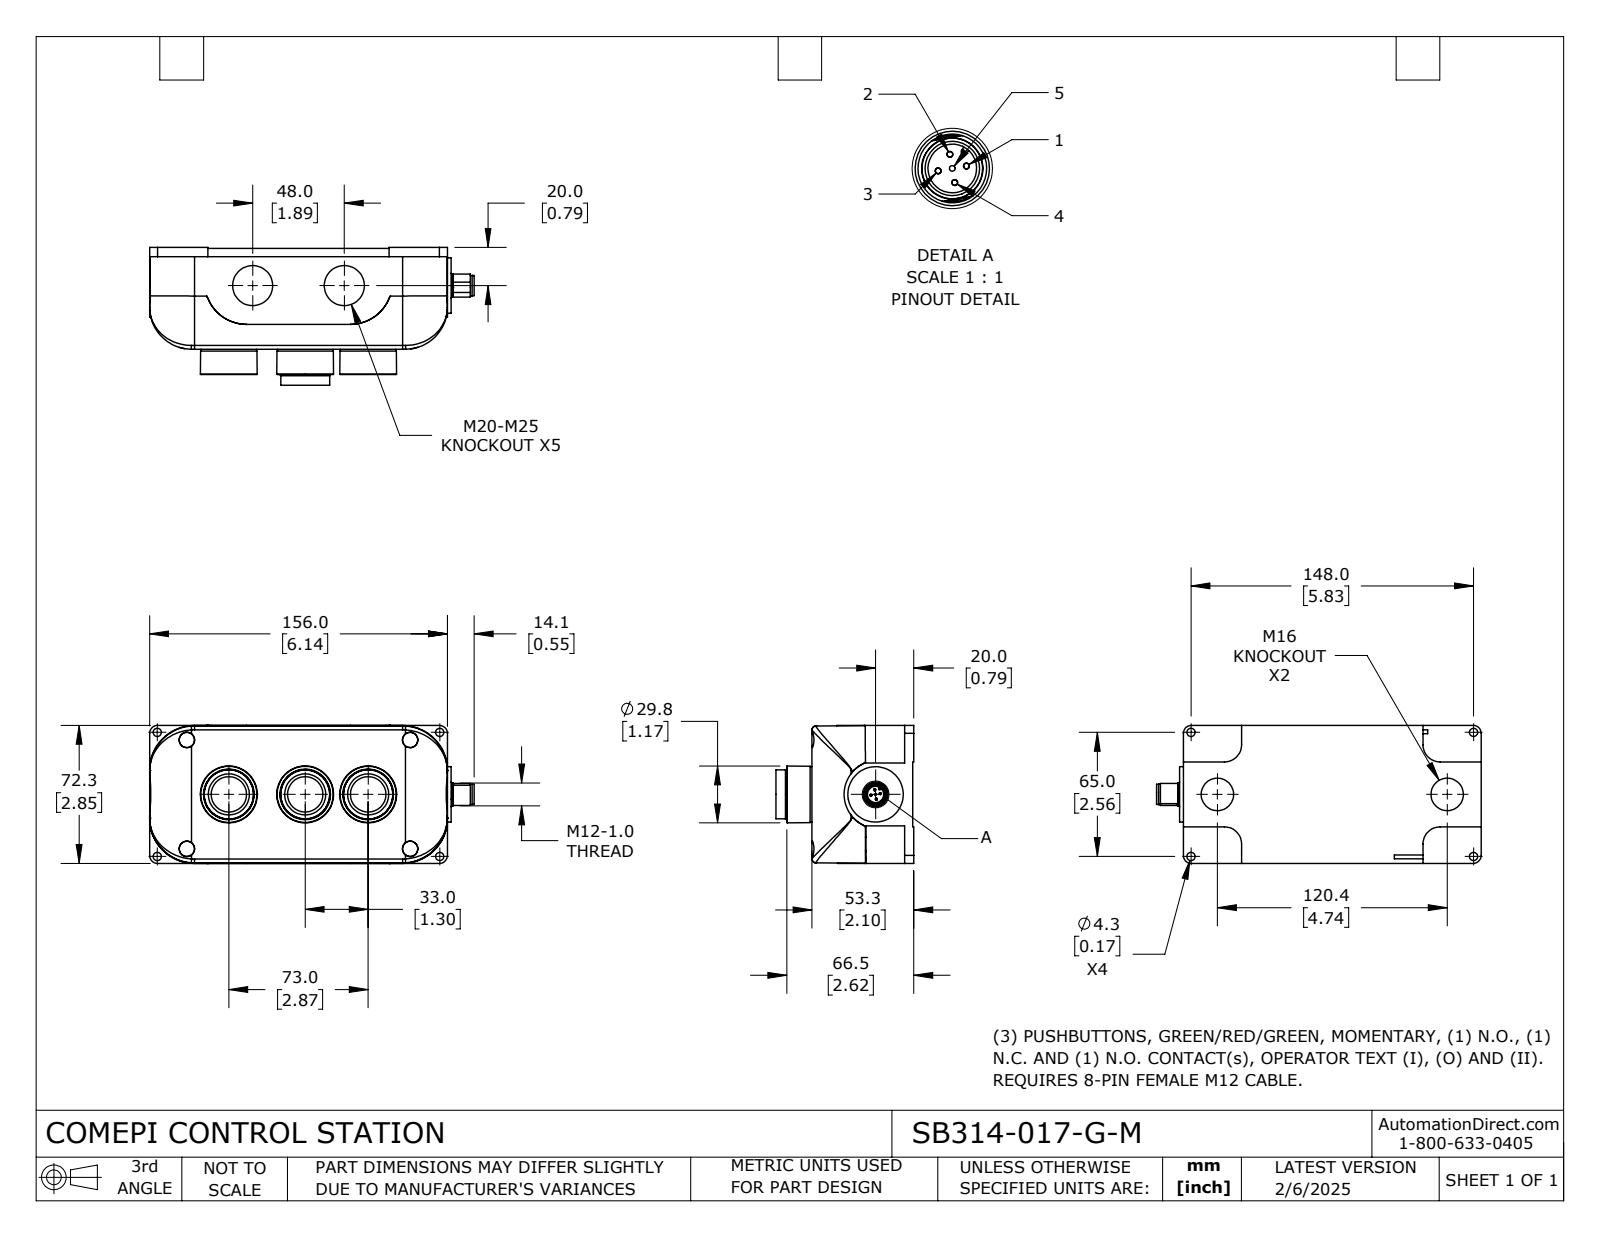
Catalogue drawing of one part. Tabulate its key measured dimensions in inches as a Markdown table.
| quantity | value |
| --- | --- |
| part name | SB314-017-G-M |
| STEP written by | SolidWorks 2024 (CONFIG_CONTROL_DESIGN) |
| units | inches |
| bodies | 16 solids, 766 faces (288 planar, 275 cylindrical, 203 other) |
| overall size | 6.695 × 2.846 × 2.843 |
| volume | 19.86 in³ |
| surface area | 165.5 in² |
| round holes (diameter × count) | 0.04 × 4, 0.067 × 4, 0.087 × 4, 0.169 × 4, 0.531 × 3, 0.827 × 3, 0.854 × 3, 0.669 × 2, 0.335 × 1, 0.713 × 1, 0.89 × 1 |
| round bosses / shafts (diameter × count) | 0.039 × 5, 1.142 × 4, 0.085 × 4, 0.065 × 4, 0.748 × 3, 0.63 × 3, 0.614 × 3, 1.016 × 2 |
| partial cylindrical surfaces (radius × count) | 0.01 × 6, 0.02 × 5, 0.035 × 4, 0.079 × 4, 0.157 × 4, 0.354 × 4, 0.38 × 4, 0.866 × 4 |
| main face-to-face distances | 0.098, 2.079, 1.98, 0.118, 0.512, 1.567, 1.469, 0.591, 0.976, 0.878 |
| hole center spacings | 1.39, 1.954, 4.535, 5.436, 0.098, 0.139, 0.139, 0.933 |
